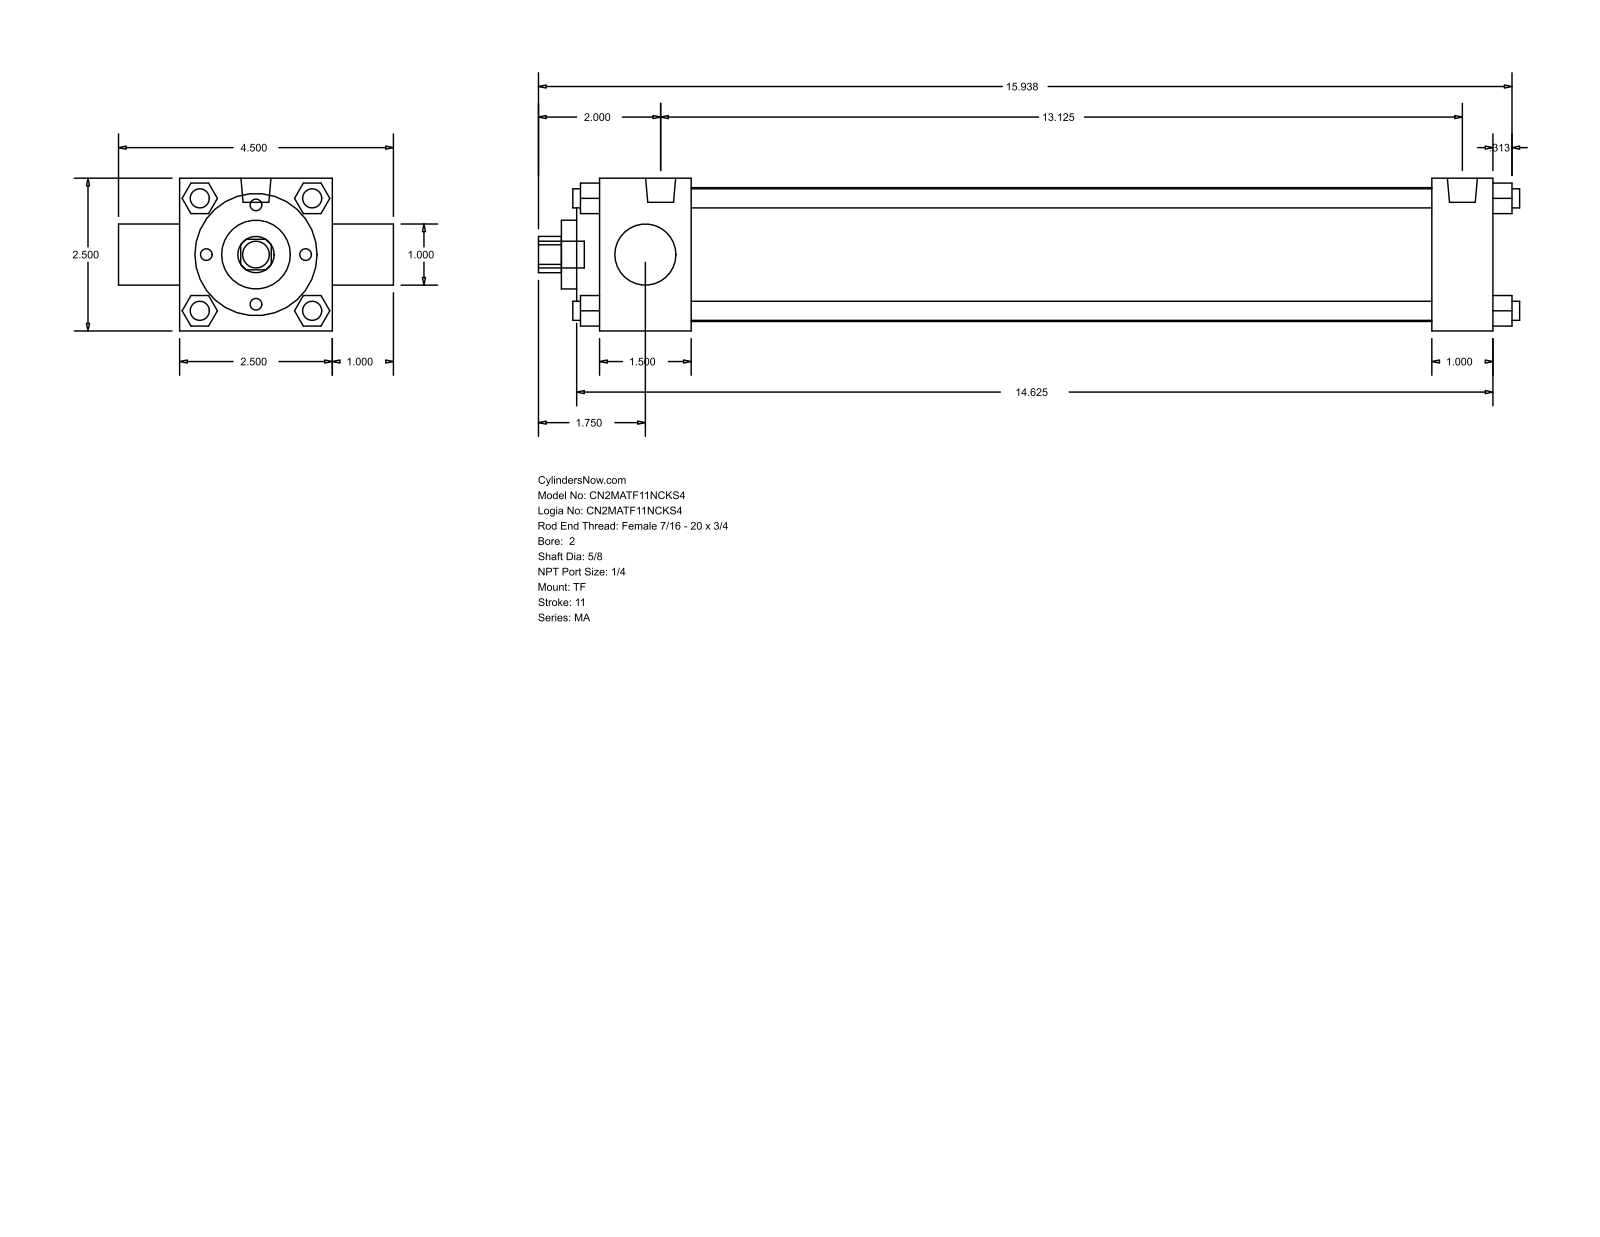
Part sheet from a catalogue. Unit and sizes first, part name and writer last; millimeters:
Units: millimetres
Overall size (bounding box): 407.99 × 114.3 × 63.5
Round holes (diameter × count): ⌀15.88 ×1, ⌀25.4 ×1, ⌀28.57 ×1, ⌀50.8 ×1, ⌀55.63 ×1
Round bosses / shafts (diameter × count): ⌀7.94 ×7, ⌀12.49 ×2, ⌀11.11 ×1
Partial cylindrical surfaces — rounded edges, fillets, slot ends (radius × count): R7.54 ×1
Main face-to-face distances: 63.5, 25.4, 38.1, 12.7, 371.48, 9.52, 346.08, 307.98, 333.38, 47.62
Bodies: 0 solids, 122 faces (93 planar, 29 cylindrical, 0 other)
Part name (STEP PRODUCT): MA_TF__0200_0.625
STEP written by: GSSL Pune (CONFIG_CONTROL_DESIGN)
